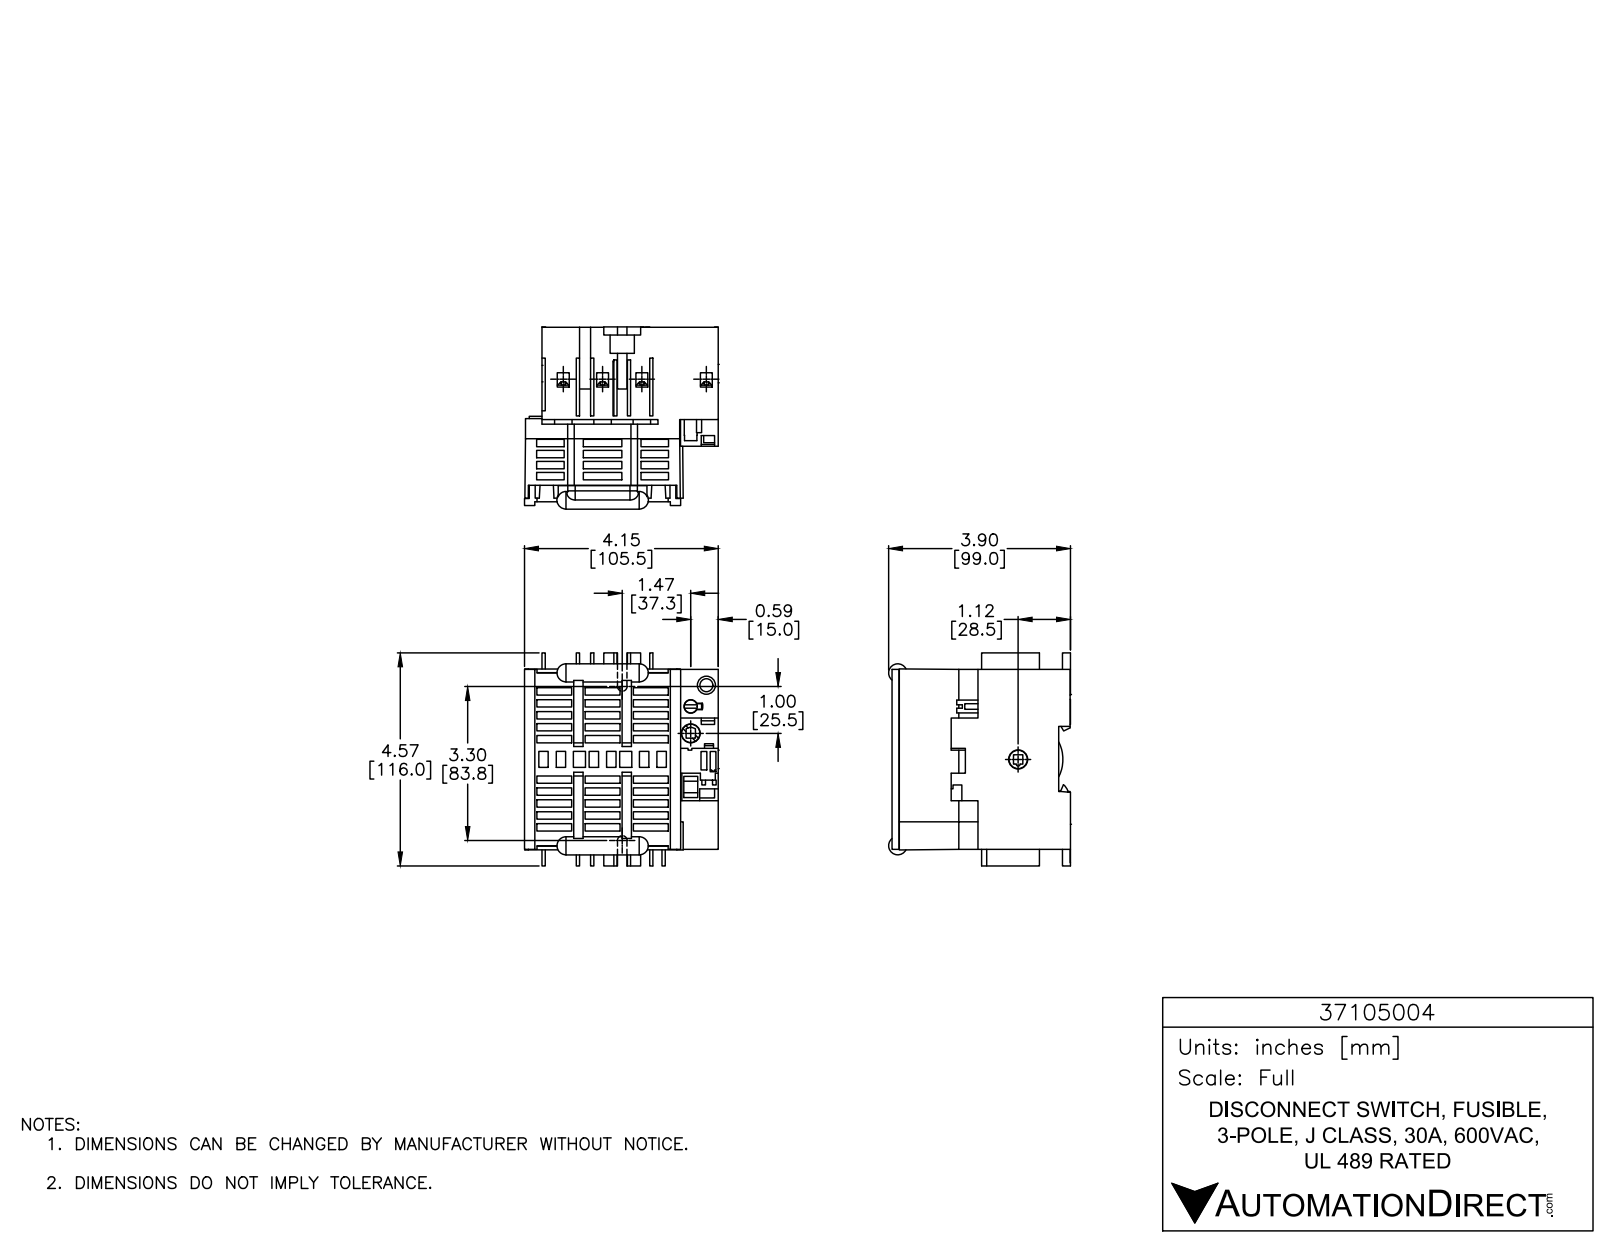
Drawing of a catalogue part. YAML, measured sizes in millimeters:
part_name: "37105004"
step_written_by: "SolidWorks 2015 (AUTOMOTIVE_DESIGN)"
units: millimeters
bodies: {solids: 3, faces: 2210, planar: 1893, cylindrical: 272, other: 45}
overall_size: [116, 105.5, 99.2]
volume: 527500
surface_area: 137400
round_holes:
  - {diameter: 7, count: 10}
  - {diameter: 3.7, count: 4}
  - {diameter: 2.2, count: 3}
  - {diameter: 4.2, count: 1}
  - {diameter: 7.3, count: 1}
  - {diameter: 9.2, count: 1}
  - {diameter: 9.8, count: 1}
  - {diameter: 10.2, count: 1}
  - {diameter: 10.4, count: 1}
round_bosses_or_shafts:
  - {diameter: 9.5, count: 4}
  - {diameter: 10, count: 2}
  - {diameter: 9, count: 1}
  - {diameter: 7, count: 1}
partial_cylinders:
  - {radius: 0.5, count: 27}
  - {radius: 0.3, count: 20}
  - {radius: 1, count: 12}
  - {radius: 5, count: 12}
  - {radius: 7, count: 12}
  - {radius: 1.3, count: 8}
  - {radius: 1.5, count: 8}
  - {radius: 3, count: 5}
face_to_face_distances: [1.8, 2, 96, 32.4, 60.6, 93, 98, 44.8, 95, 34.4]
hole_center_spacings: [21.4, 10.9, 83.2, 83.5, 42.8, 80.7, 9.5, 20.1]
